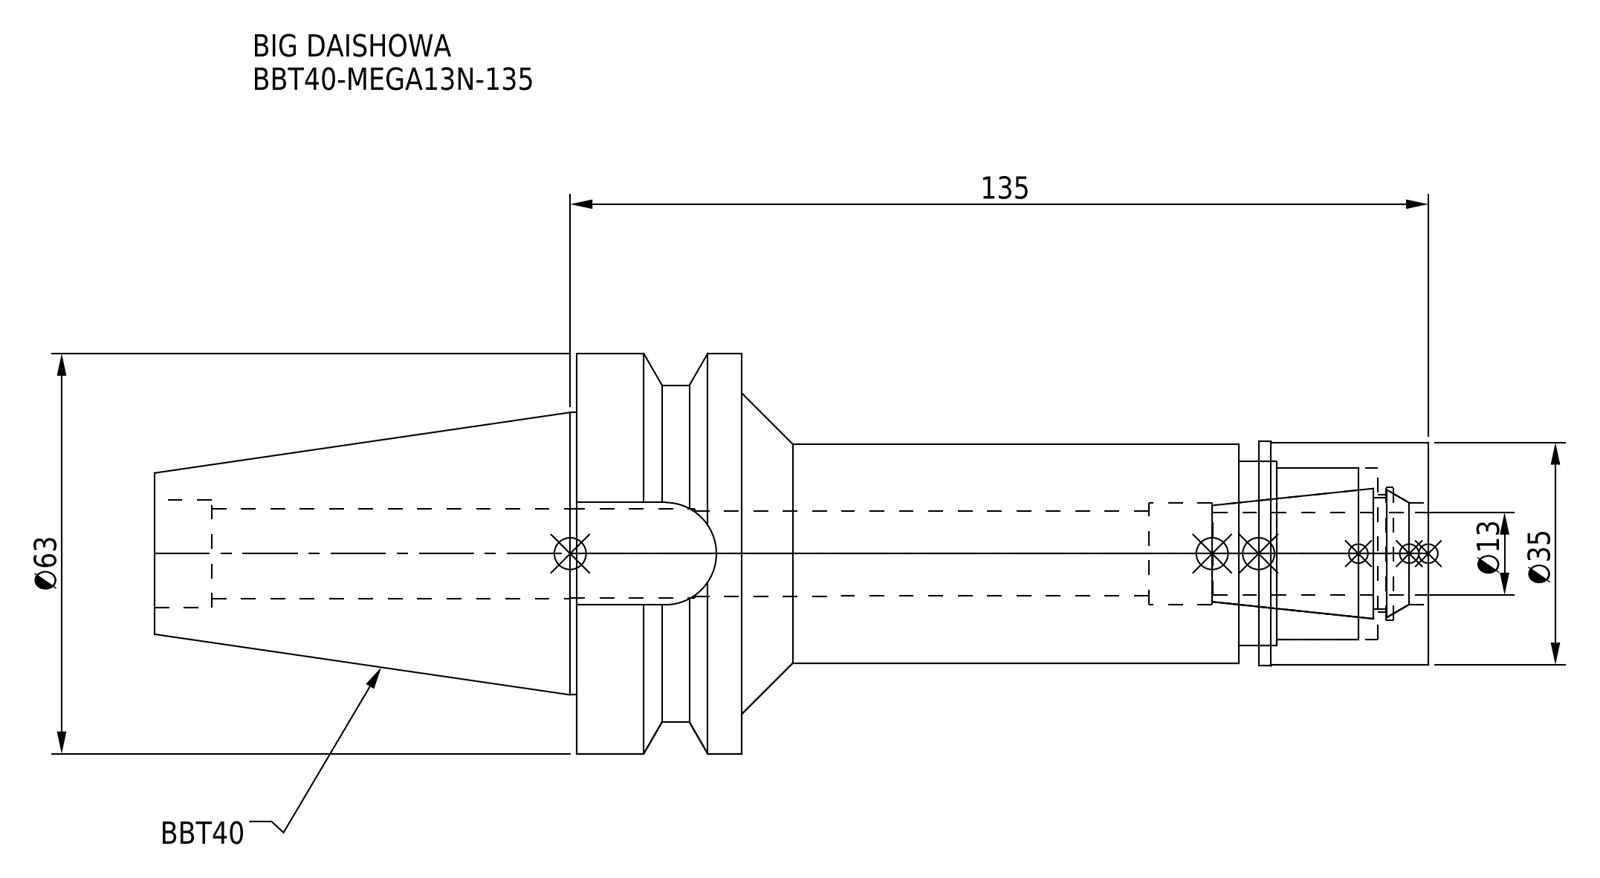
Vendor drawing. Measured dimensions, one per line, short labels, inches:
name: BBT40MN13135-130_ASM.stp; BBT40-MEGA13N-135_1.stp; MGN13_1.stp; BBT40-MEGA13N-135 (+3 more)
written by: SolidWorks 2019 (CONFIG_CONTROL_DESIGN)
unit: in
bodies: 2 solids, 80 faces (24 planar, 42 cylindrical, 14 other)
size: 7.89 × 2.48 × 2.48
volume: 12.52 in³; area: 67.25 in²
holes: 1× ⌀0.524, 1× ⌀0.531, 1× ⌀0.551, 1× ⌀0.559, 1× ⌀0.63, 1× ⌀0.669, 1× ⌀0.728, 1× ⌀0.827, 1× ⌀1.063, 1× ⌀1.142
bosses: 1× ⌀2.48, 1× ⌀2.087, 1× ⌀1.75, 1× ⌀1.39, 1× ⌀1.378, 1× ⌀1.358
rounds: 1× R0.317
face distances: 1.024, 4.252, 5.276, 1.772, 3.937, 1.051, 3.201, 4.224, 0.315, 0.736
